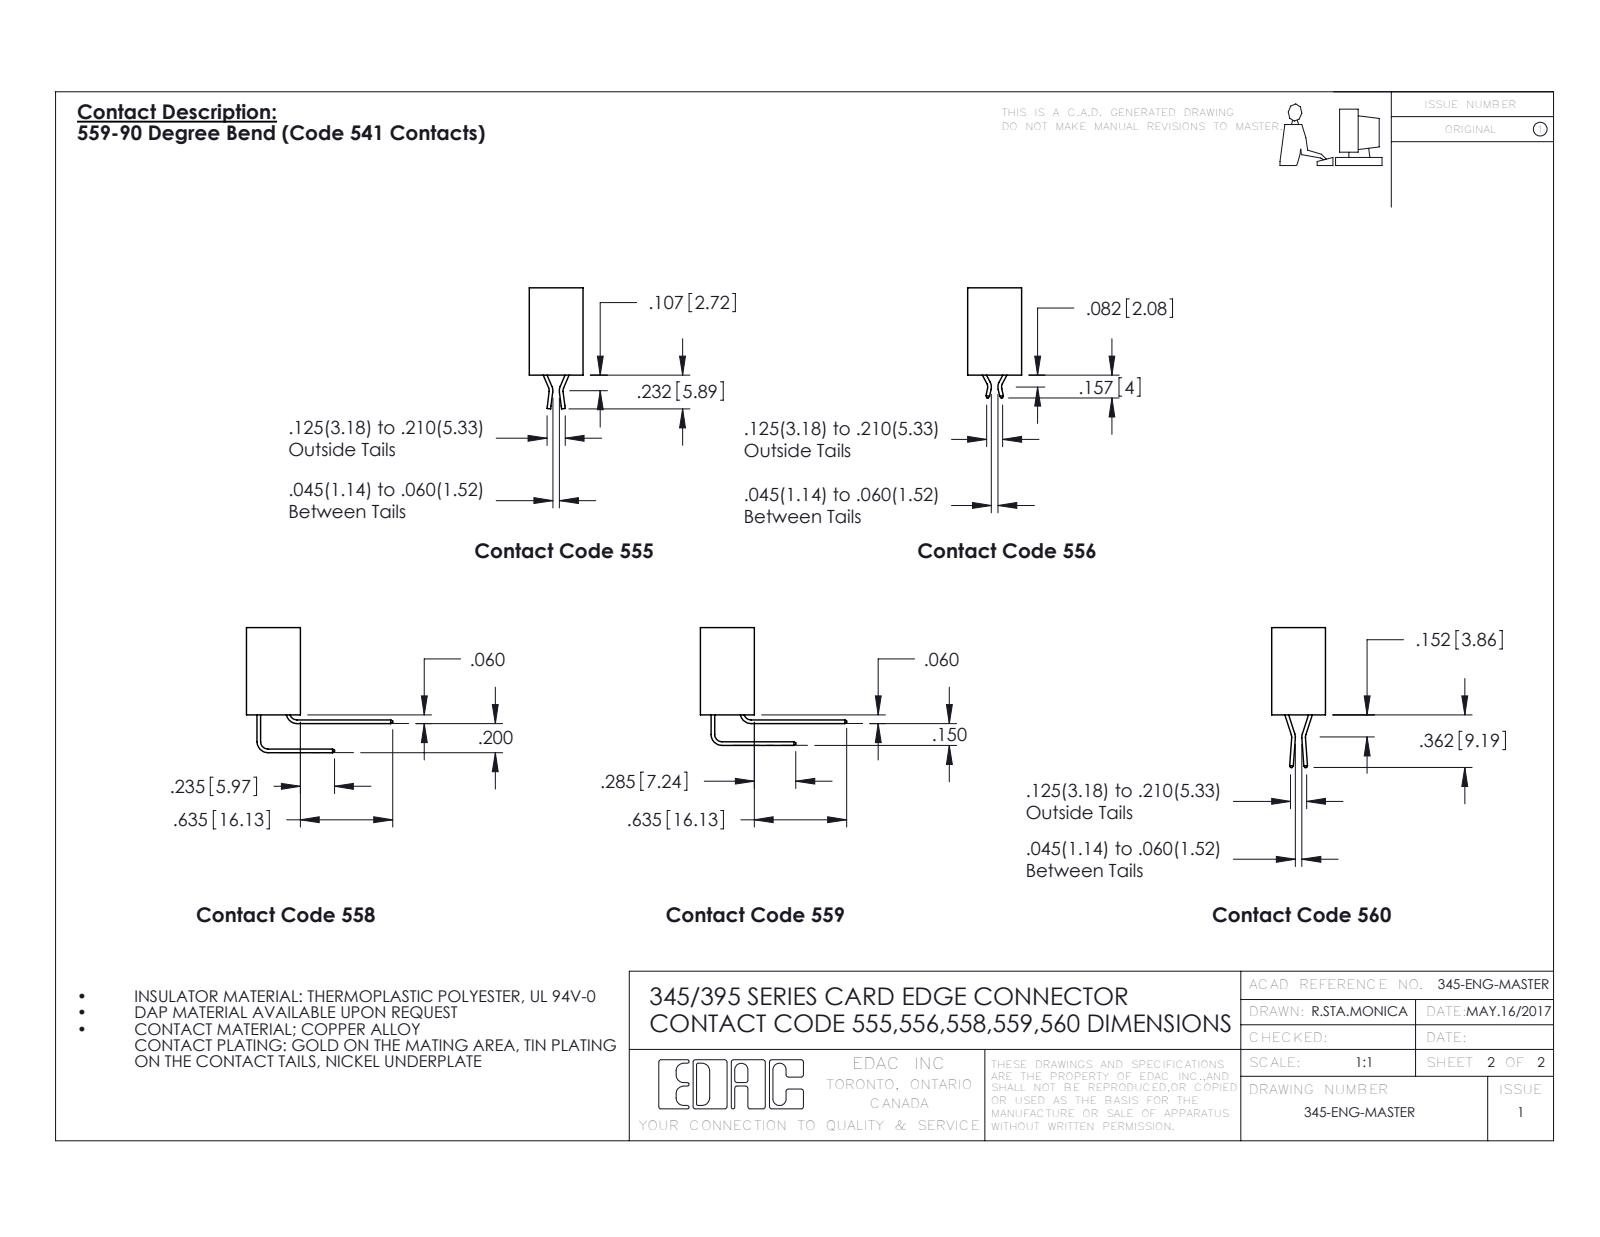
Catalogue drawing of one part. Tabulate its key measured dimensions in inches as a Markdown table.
| quantity | value |
| --- | --- |
| part name | 345-292-001_560 Tail; 345 Part_No Mounting Lugs; 395-018-560-201 |
| STEP written by | SolidWorks 2016 (CONFIG_CONTROL_DESIGN) |
| units | inches |
| bodies | 19 solids, 1054 faces (670 planar, 384 cylindrical, 0 other) |
| overall size | 1.16 × 0.962 × 0.37 |
| volume | 0.201 in³ |
| surface area | 7.487 in² |
| round holes (diameter × count) | 0.064 × 1 |
| partial cylindrical surfaces (radius × count) | 0.006 × 27, 0.01 × 22, 0.007 × 6, 0.031 × 6, 0.026 × 3, 0.01 × 2, 0.014 × 2, 0.019 × 2 |
| main face-to-face distances | 0.2, 0.025, 0.298, 0.072, 0.1, 0.37, 0.3, 0.4, 0.098, 0.272 |
